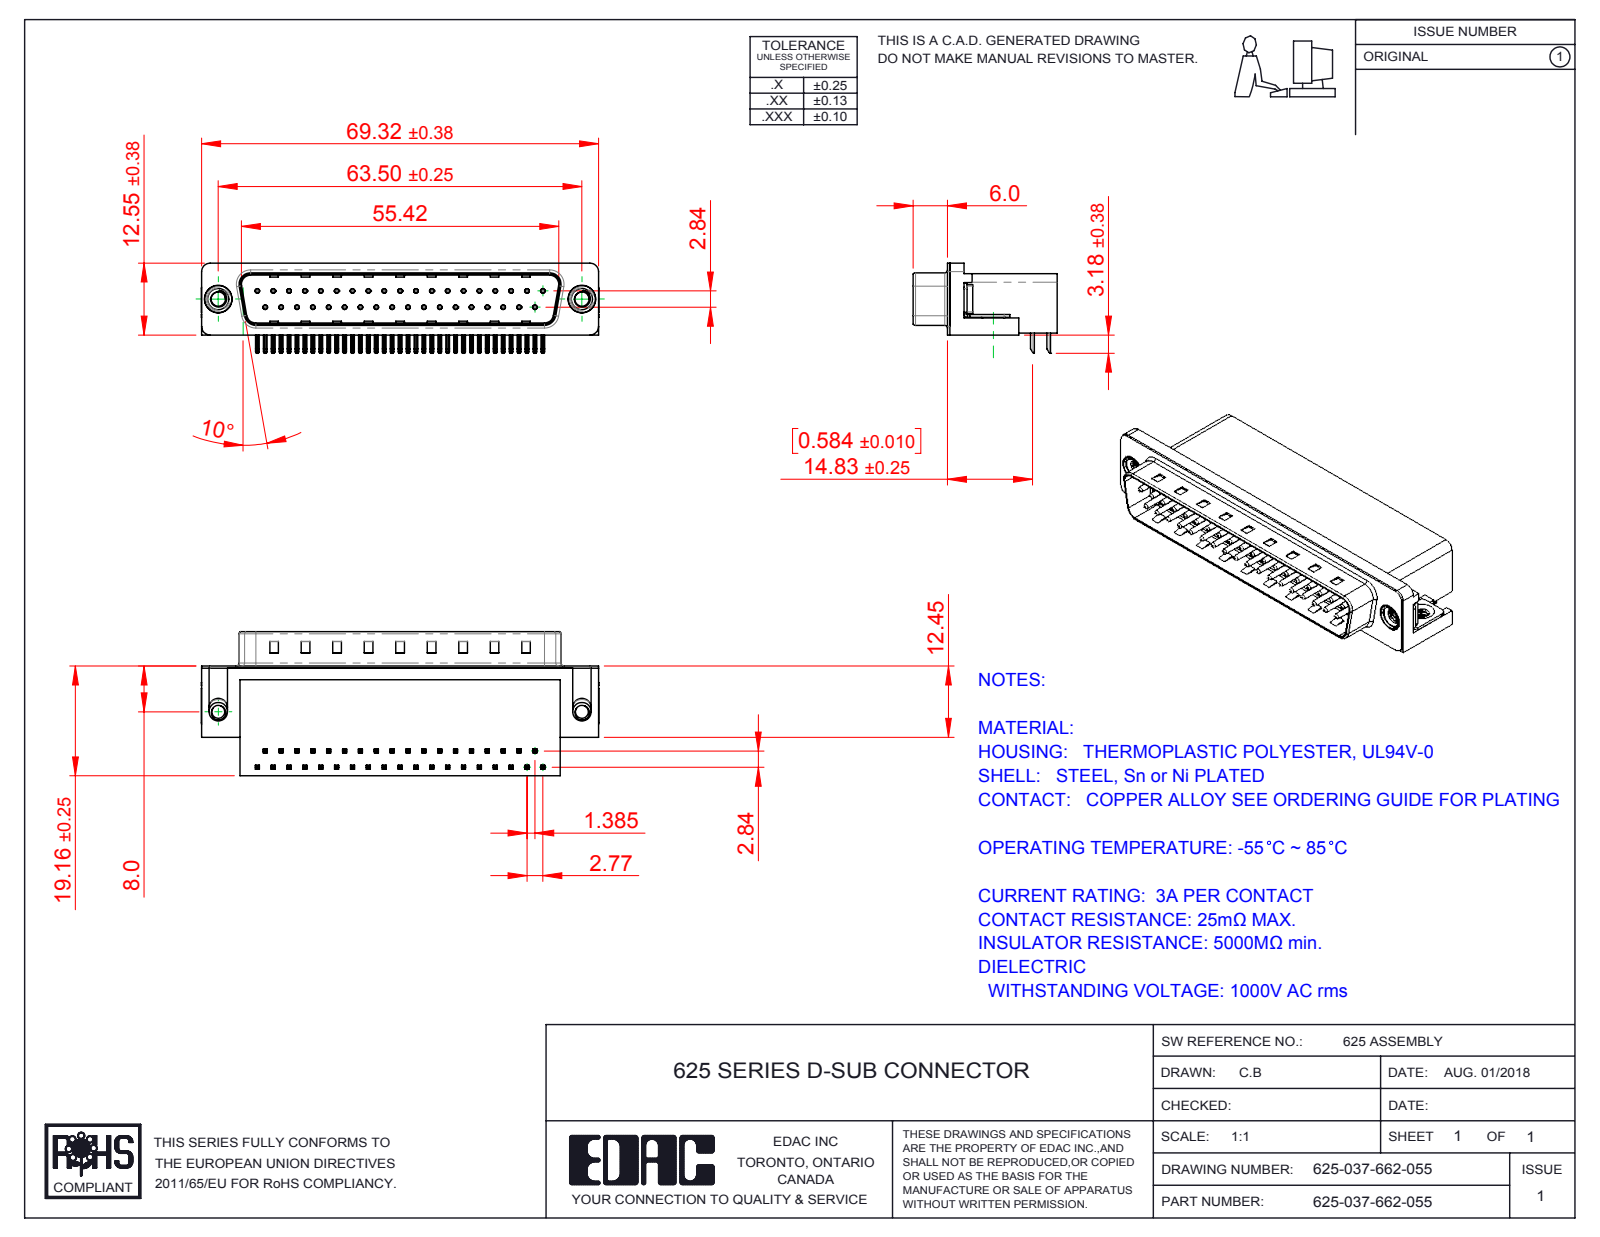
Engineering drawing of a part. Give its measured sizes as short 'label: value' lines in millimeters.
name: 625 Housing_37 Socket; 625-037-662-055; 625 4-40 Threaded Board Mount; 625 M3 Threaded Rivet (+3 more)
written by: SolidWorks 2016 (CONFIG_CONTROL_DESIGN)
unit: mm
bodies: 43 solids, 3233 faces (2015 planar, 933 cylindrical, 285 other)
size: 69.4 × 25.16 × 15.73
volume: 12 606 mm³; area: 11 837 mm²
holes: 37× ⌀0.35, 37× ⌀0.8, 2× ⌀2.26, 2× ⌀2.5, 2× ⌀4, 2× ⌀4.8, 2× ⌀5
bosses: 37× ⌀0.75, 2× ⌀4.9, 2× ⌀4.75, 2× ⌀3.9, 2× ⌀3.26
rounds: 156× R0.25, 74× R0.12, 16× R1, 9× R0.5, 8× R1.6, 7× R1.5, 4× R0.9, 4× R2
face distances: 10.34, 0.4, 18.76, 8.76, 19.16, 2.84, 2.09, 10.1, 1.74, 8.36
hole spacings: 3.16, 2.77, 5.54, 8.31, 11.08, 13.85, 19.39, 22.16
